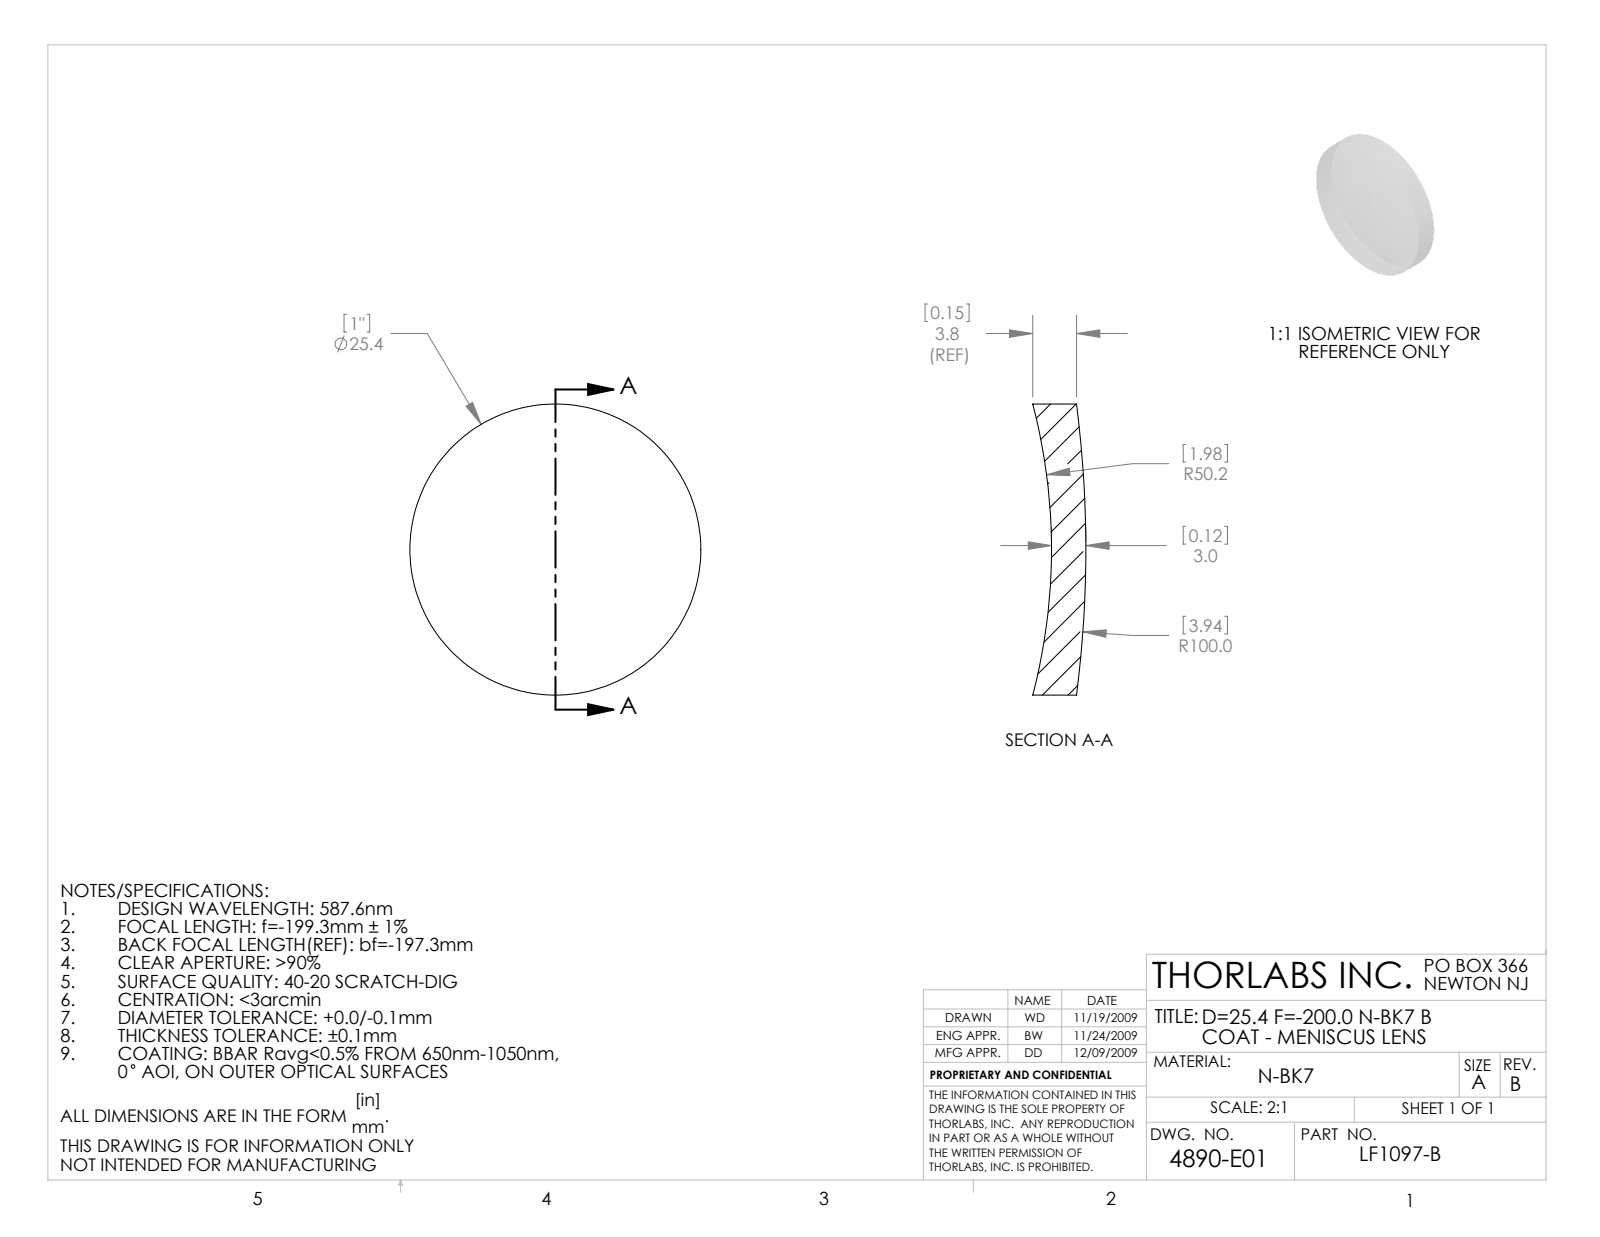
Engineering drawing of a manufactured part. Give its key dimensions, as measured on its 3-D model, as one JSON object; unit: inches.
{"part_name": "4890-E0W", "step_written_by": "SolidWorks 2009 (AUTOMOTIVE_DESIGN)", "units": "inches", "bodies": {"solids": 1, "faces": 6, "planar": 0, "cylindrical": 2, "other": 4}, "overall_size": [1, 1, 0.182], "volume_in3": 0.105, "surface_area_in2": 2.06, "round_bosses_or_shafts": [[1, 1]]}
